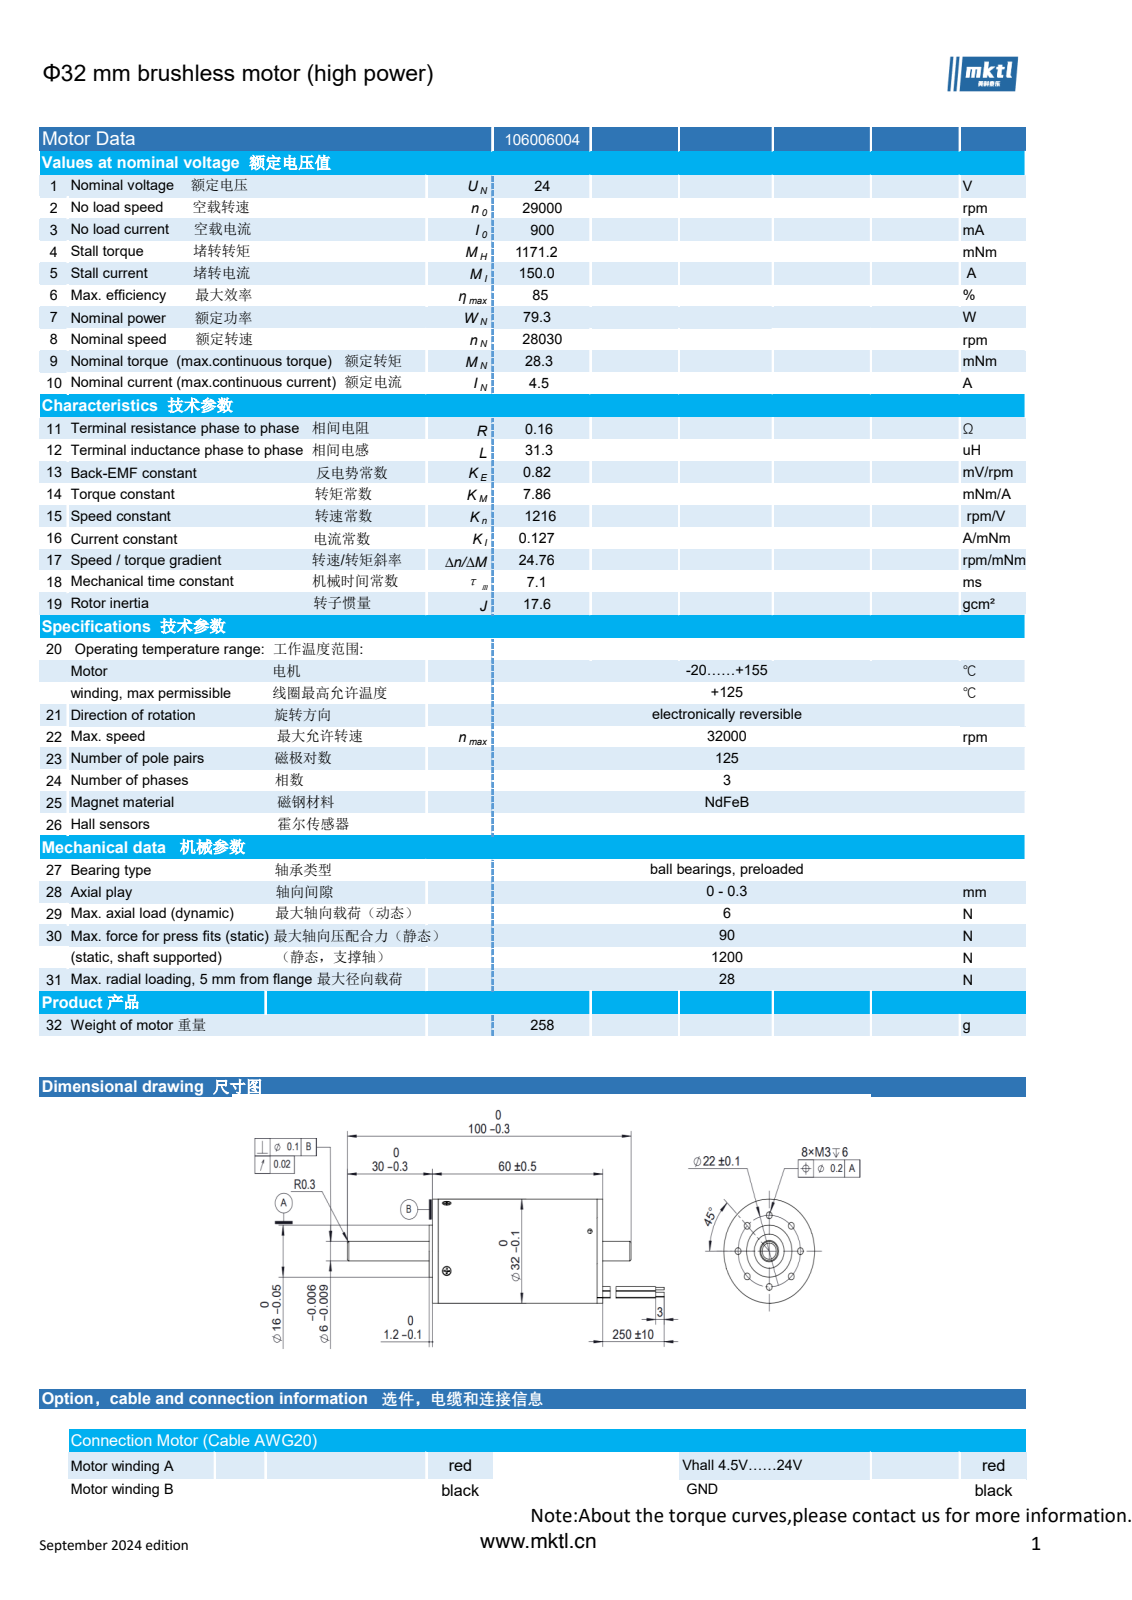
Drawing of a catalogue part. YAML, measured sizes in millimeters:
part_name: "approval 106006004"
step_written_by: "SolidWorks 2025 (AUTOMOTIVE_DESIGN)"
units: millimeters
bodies: {solids: 263, faces: 2549, planar: 931, cylindrical: 1513, other: 105}
overall_size: [111.68, 32, 32]
volume: 41931
surface_area: 148733
round_holes:
  - {diameter: 2.1, count: 11}
  - {diameter: 1.1, count: 5}
  - {diameter: 1.5, count: 5}
  - {diameter: 0.5, count: 4}
  - {diameter: 1.25, count: 4}
  - {diameter: 3.1, count: 4}
  - {diameter: 1.2, count: 3}
  - {diameter: 3, count: 3}
  - {diameter: 1.6, count: 2}
  - {diameter: 1.3, count: 1}
  - {diameter: 6, count: 1}
  - {diameter: 9, count: 1}
round_bosses_or_shafts:
  - {diameter: 1.4, count: 7}
  - {diameter: 1.2, count: 5}
  - {diameter: 0.8, count: 5}
  - {diameter: 2.8, count: 4}
  - {diameter: 1.6, count: 4}
  - {diameter: 1.3, count: 4}
  - {diameter: 4, count: 3}
  - {diameter: 1.8, count: 3}
partial_cylinders:
  - {radius: 0.1, count: 24}
  - {radius: 0.3, count: 21}
  - {radius: 0.75, count: 11}
  - {radius: 0.2, count: 5}
  - {radius: 1.5, count: 4}
  - {radius: 8, count: 2}
  - {radius: 6, count: 1}
  - {radius: 7.5, count: 1}
face_to_face_distances: [0.6, 0.4, 0.8, 1, 1.2, 1.4, 1.6, 1.8, 37, 2]
hole_center_spacings: [8.42, 11, 15.56, 20.33, 2, 12.25, 22.7, 23.62]
